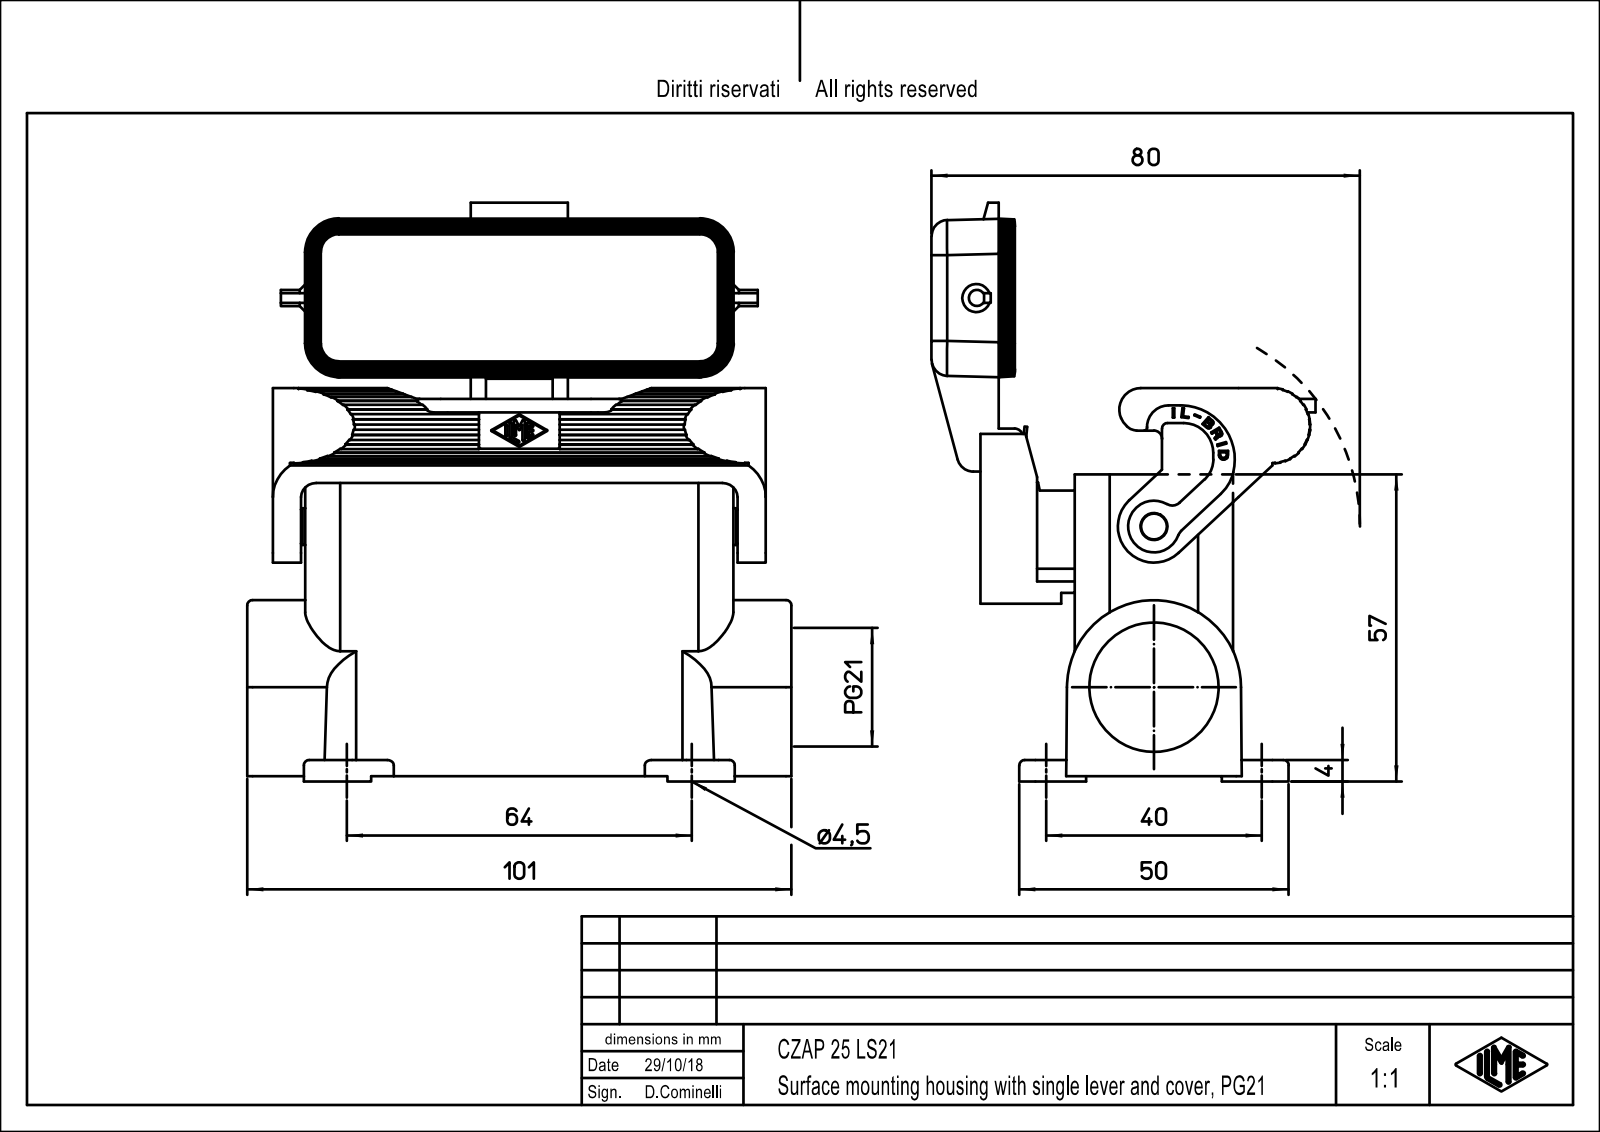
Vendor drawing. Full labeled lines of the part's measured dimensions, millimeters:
Part name (STEP PRODUCT): CZAP_25_LS21
STEP written by: PTC Creo Elements/Direct Modeling 19.0E 27-Jun-2016 (C) Parametric Technology GmbH (AUTOMOTIVE_DESIGN)
Units: millimetres
Bodies: 1 solid, 849 faces (591 planar, 215 cylindrical, 43 other)
Overall size (bounding box): 107.4 × 101 × 71.3
Volume: 86 608 mm³ · Surface area: 56 504 mm²
Round holes (diameter × count): ⌀3 ×4, ⌀4.5 ×4, ⌀5 ×1, ⌀22 ×1, ⌀27.12 ×1
Round bosses / shafts (diameter × count): ⌀7 ×1, ⌀6.8 ×1, ⌀4.8 ×1, ⌀3 ×1
Partial cylindrical surfaces — rounded edges, fillets, slot ends (radius × count): R1 ×17, R0.2 ×15, R3 ×12, R3.5 ×12, R6.5 ×8, R0.5 ×7, R3.2 ×4, R6 ×4
Main face-to-face distances: 2.76, 26.64, 29.4, 23.88, 56, 2, 3, 54, 51.24, 27.36
Hole centre spacings: 12.04, 28.02, 66.1, 70.77, 16, 40, 64, 66
